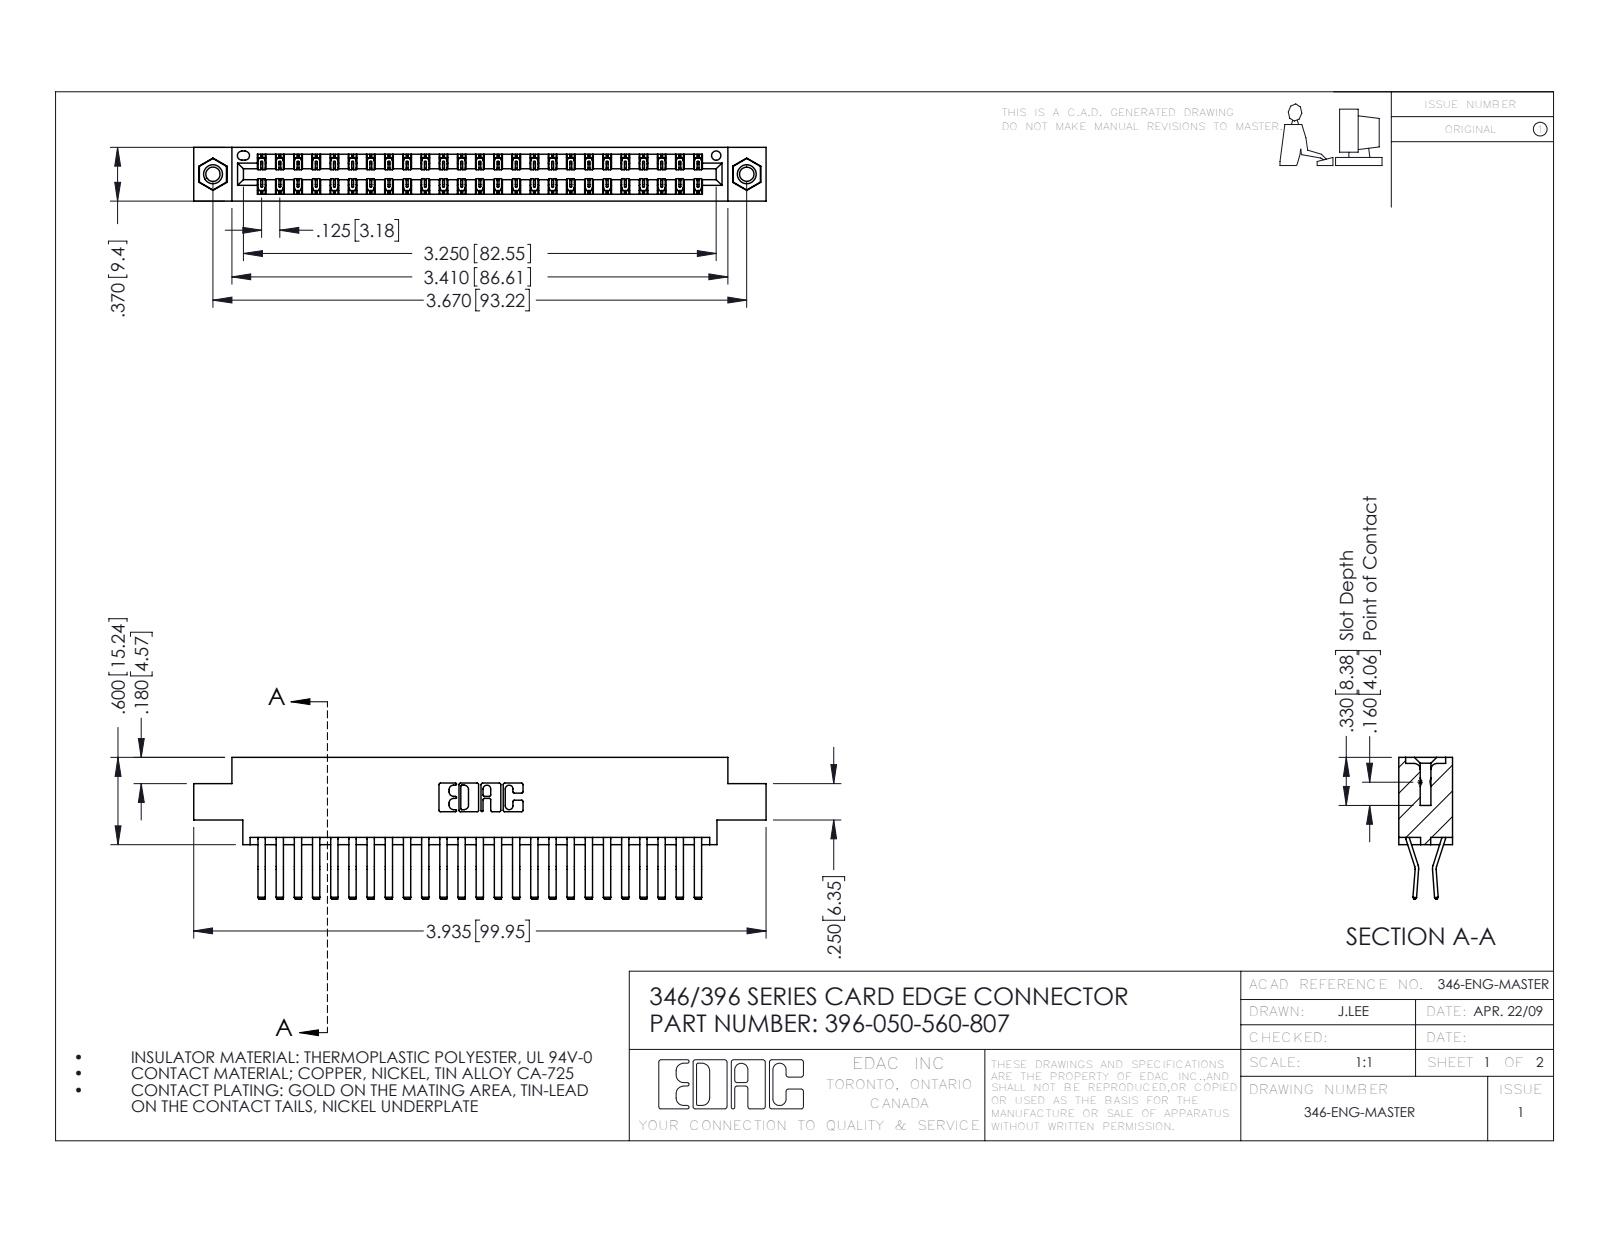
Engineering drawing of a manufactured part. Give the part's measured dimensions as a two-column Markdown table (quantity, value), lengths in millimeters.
| quantity | value |
| --- | --- |
| part name | 345-292-001_560 Tail; 396-050-560-807; 346 Part_0.170 Offset - 0.156 Dia-TI; 345-250-001_345-250-005-103 |
| STEP written by | SolidWorks 2016 (CONFIG_CONTROL_DESIGN) |
| units | millimeters |
| bodies | 53 solids, 2886 faces (1862 planar, 1008 cylindrical, 16 other) |
| overall size | 99.9 × 24.8 × 9.4 |
| volume | 9 770 mm³ |
| surface area | 14 260 mm² |
| round holes (diameter × count) | 2.5 × 2, 3.2 × 2, 4 × 2, 1.6 × 1 |
| round bosses / shafts (diameter × count) | 3.9 × 2 |
| partial cylindrical surfaces (radius × count) | 0.2 × 75, 0.3 × 22, 0.2 × 6, 0.8 × 6, 0.7 × 3, 0.3 × 2, 0.4 × 2, 0.6 × 2 |
| main face-to-face distances | 1.2, 8.2, 9.4, 0.6, 6.4, 1.8, 7.6, 7, 5.6, 3.8 |
| hole center spacings | 6.2, 87.9, 93.2 |
